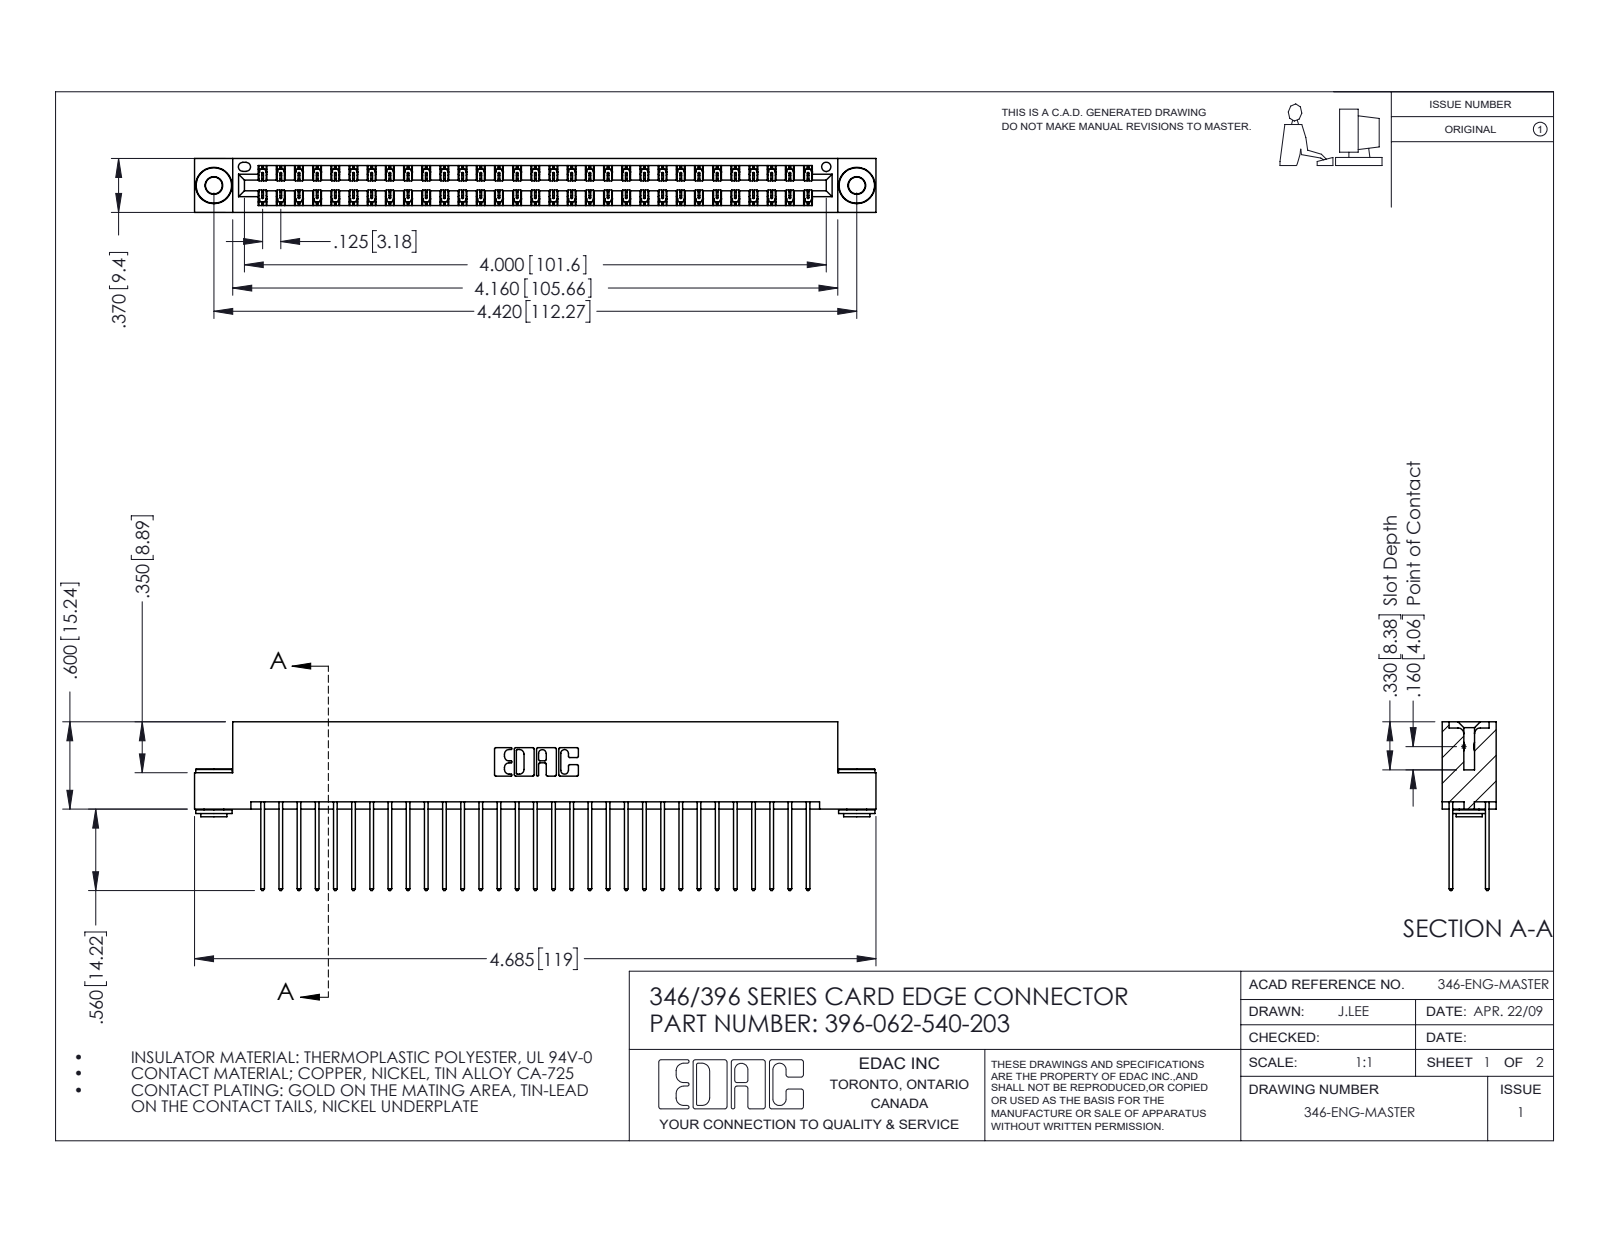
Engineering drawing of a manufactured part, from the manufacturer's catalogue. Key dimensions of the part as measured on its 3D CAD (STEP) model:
Part name (STEP PRODUCT): 345-292-001_345-293-140; 345-250-002_345-250-002-102; 396-062-540-203; 346 Part_Flush Mounting Lugs - 0.156 Dia-TH
STEP written by: SolidWorks 2016 (CONFIG_CONTROL_DESIGN)
Units: inches
Bodies: 65 solids, 3384 faces (2256 planar, 1120 cylindrical, 8 other)
Overall size (bounding box): 4.685 × 1.16 × 0.37
Volume: 0.718 in³ · Surface area: 26.87 in²
Round holes (diameter × count): ⌀0.116 ×2, ⌀0.156 ×2, ⌀0.064 ×1
Round bosses / shafts (diameter × count): ⌀0.25 ×2, ⌀0.18 ×2, ⌀0.136 ×2
Partial cylindrical surfaces — rounded edges, fillets, slot ends (radius × count): R0.006 ×93, R0.01 ×62, R0.01 ×22, R0.007 ×6, R0.031 ×6, R0.026 ×3, R0.014 ×2, R0.022 ×2
Main face-to-face distances: 0.048, 0.322, 0.25, 0.025, 0.072, 0.298, 0.37, 0.275, 0.148, 0.222
Hole centre spacings: 0.246, 4.212, 4.42
